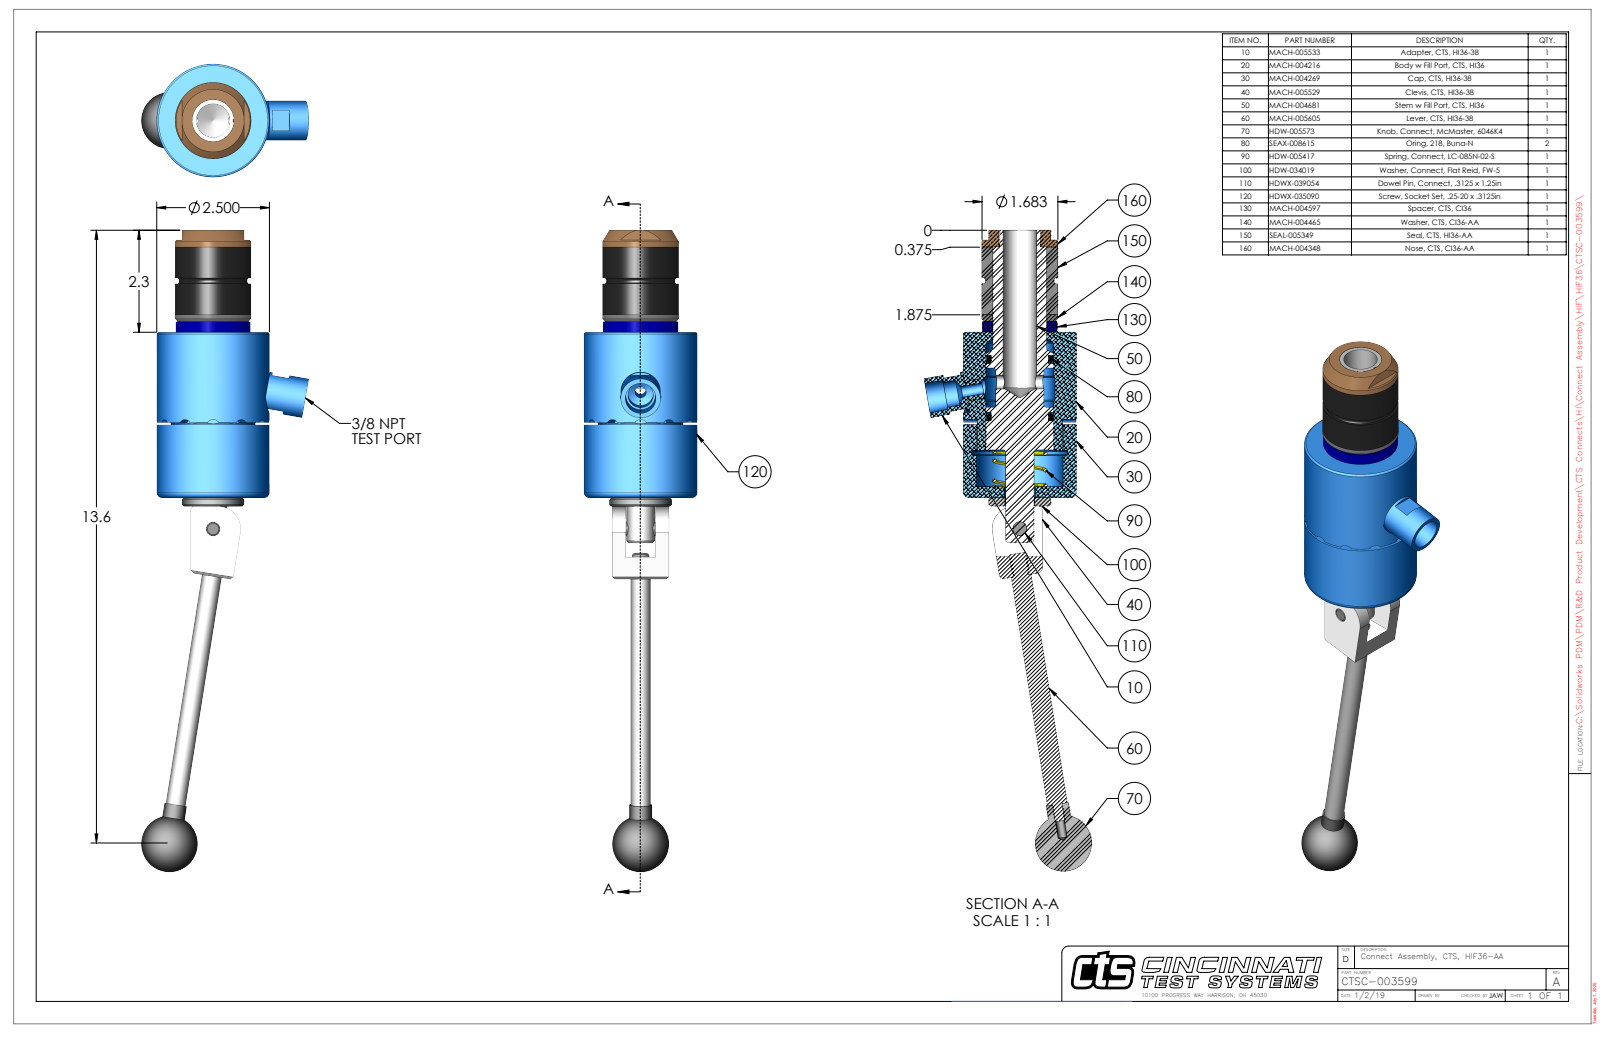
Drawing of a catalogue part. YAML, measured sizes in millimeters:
part_name: "CTSC-003599"
step_written_by: "SolidWorks 2023 (AUTOMOTIVE_DESIGN)"
units: millimeters
bodies: {solids: 10, faces: 413, planar: 182, cylindrical: 131, other: 100}
overall_size: [361.1, 94.4, 63.5]
volume: 408400
surface_area: 82000
round_holes:
  - {diameter: 5.1, count: 2}
  - {diameter: 3.8, count: 1}
  - {diameter: 6.4, count: 1}
  - {diameter: 7.9, count: 1}
  - {diameter: 7.9, count: 1}
  - {diameter: 8, count: 1}
  - {diameter: 8, count: 1}
  - {diameter: 14.3, count: 1}
  - {diameter: 16.7, count: 1}
  - {diameter: 17.7, count: 1}
  - {diameter: 19.1, count: 1}
  - {diameter: 23.4, count: 1}
round_bosses_or_shafts:
  - {diameter: 63.5, count: 1}
  - {diameter: 47.6, count: 1}
  - {diameter: 42.7, count: 1}
  - {diameter: 42.1, count: 1}
  - {diameter: 35.1, count: 1}
  - {diameter: 30.1, count: 1}
  - {diameter: 25.4, count: 1}
  - {diameter: 23, count: 1}
partial_cylinders:
  - {radius: 3, count: 12}
  - {radius: 0.7, count: 2}
  - {radius: 4.8, count: 1}
  - {radius: 5, count: 1}
  - {radius: 11, count: 1}
  - {radius: 11.9, count: 1}
  - {radius: 12.7, count: 1}
  - {radius: 29.8, count: 1}
face_to_face_distances: [93.2, 141.1, 47.9, 38.1, 103, 9.8, 7.5, 24.2, 41.1, 52]
hole_center_spacings: [18.8, 53.8, 72.6]
